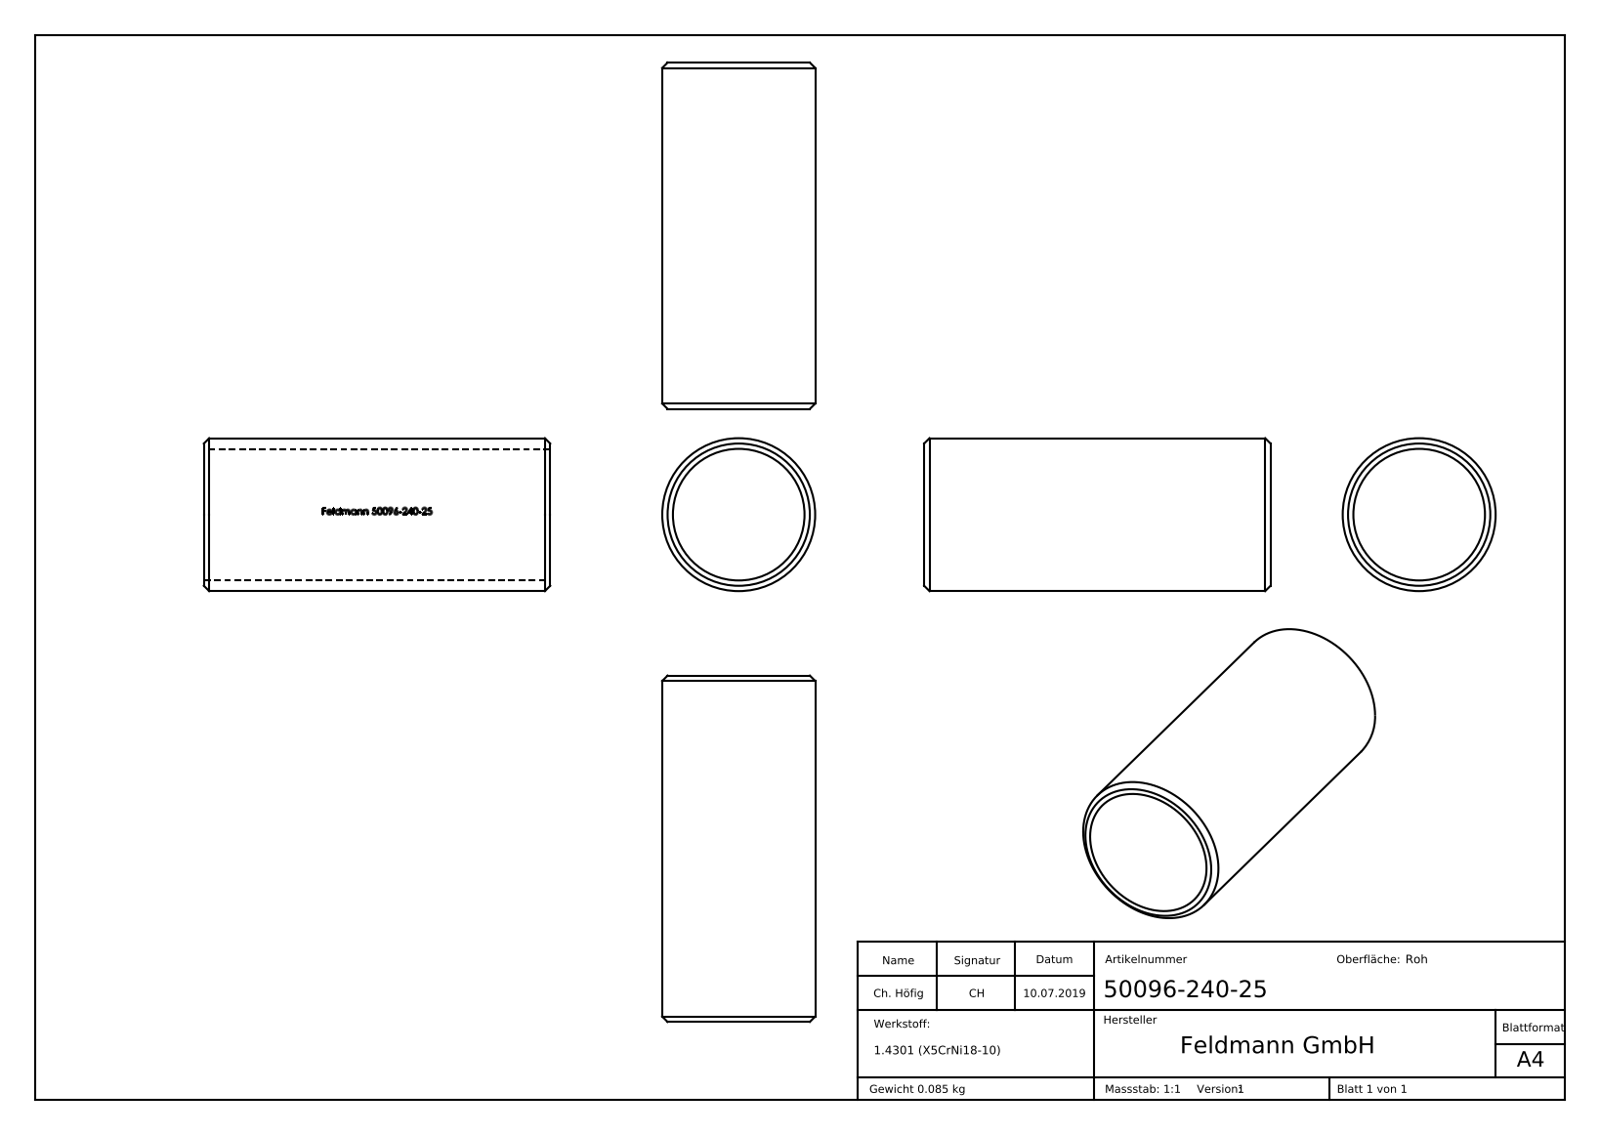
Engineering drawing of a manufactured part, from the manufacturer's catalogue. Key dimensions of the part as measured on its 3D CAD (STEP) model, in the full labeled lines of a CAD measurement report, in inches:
Part name (STEP PRODUCT): 50096-240-25
STEP written by: SolidWorks 2015 (CONFIG_CONTROL_DESIGN)
Units: inches
Bodies: 1 solid, 281 faces (107 planar, 49 cylindrical, 125 other)
Overall size (bounding box): 2.559 × 1.13 × 1.13
Volume: 0.66 in³ · Surface area: 17.27 in²
Round holes (diameter × count): ⌀0.972 ×1
Round bosses / shafts (diameter × count): ⌀1.13 ×1
Partial cylindrical surfaces — rounded edges, fillets, slot ends (radius × count): R0.49 ×1
Main face-to-face distances: 2.559, 0.017, 0.015, 0.052, 0.08, 0.035, 0.023, 0.05, 0.576, 0.065
